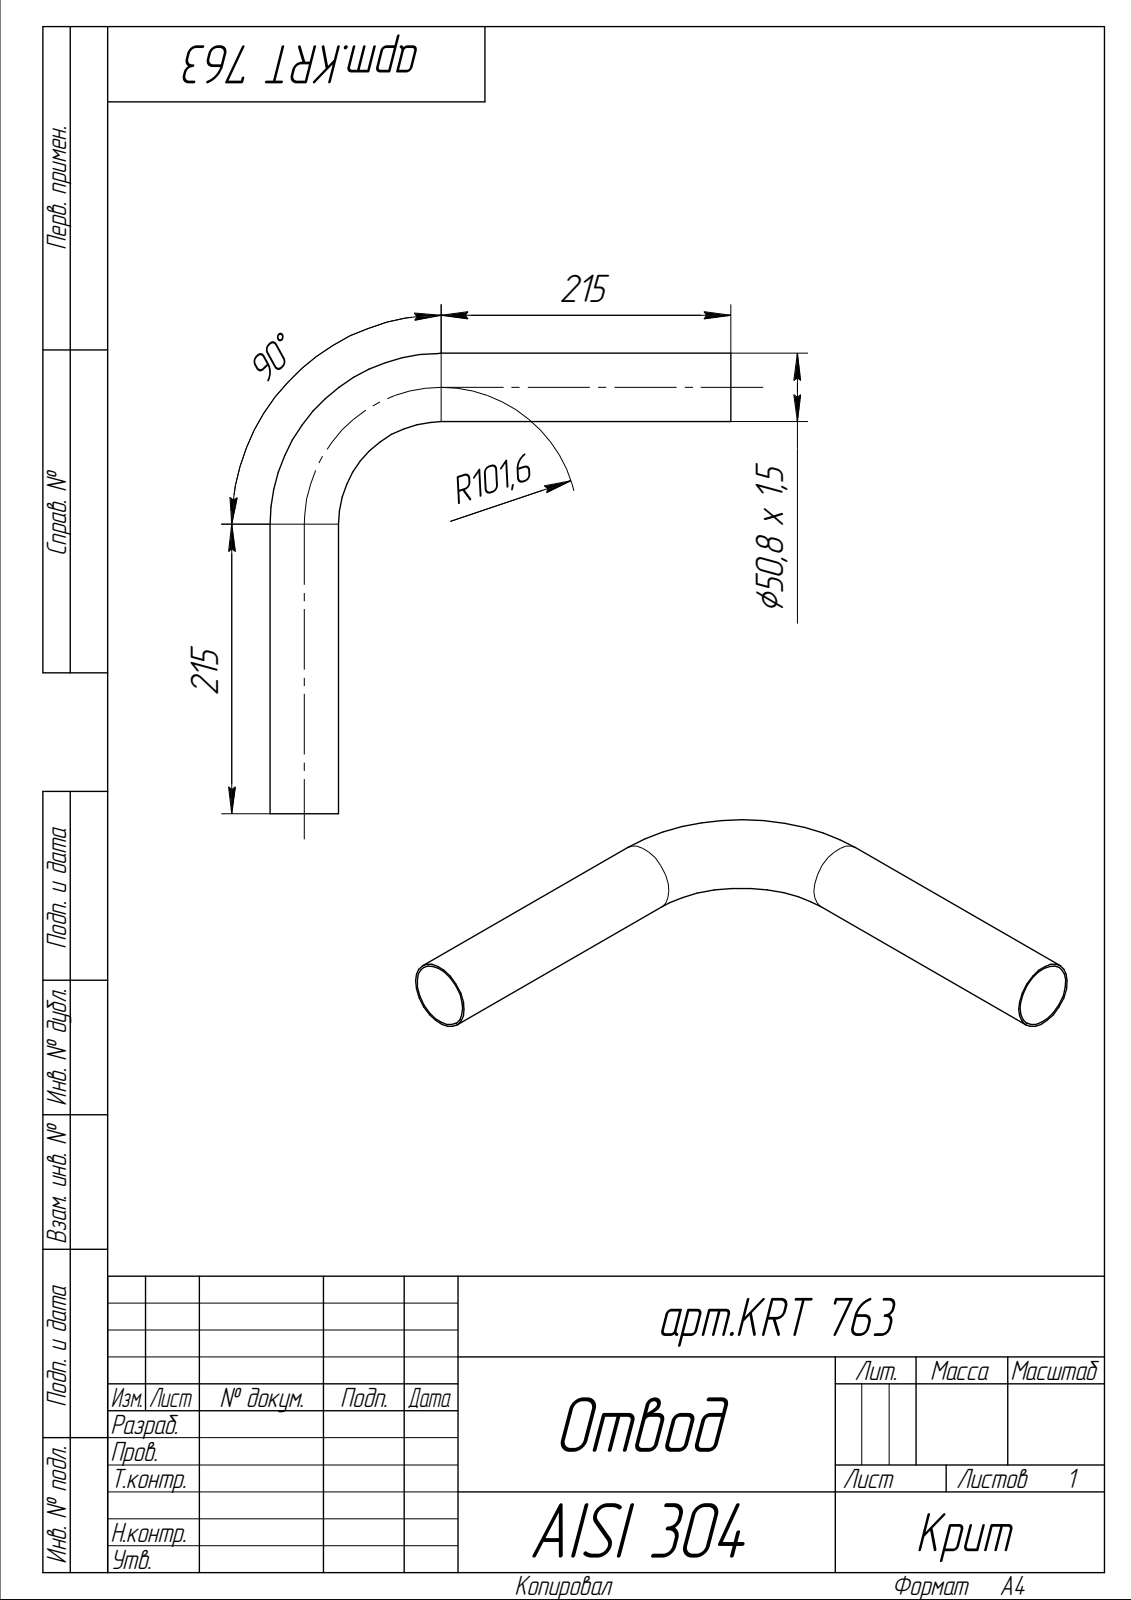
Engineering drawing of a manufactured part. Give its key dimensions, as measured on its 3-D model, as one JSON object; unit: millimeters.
{"part_name": "Деталь", "step_written_by": "ASCON Math Kernel (AUTOMOTIVE_DESIGN)", "units": "millimeters", "bodies": {"solids": 1, "faces": 8, "planar": 2, "cylindrical": 4, "other": 2}, "overall_size": [342, 342, 50.8], "volume_mm3": 136975, "surface_area_mm2": 183098, "round_holes": [[47.8, 2]], "round_bosses_or_shafts": [[50.8, 2]]}
